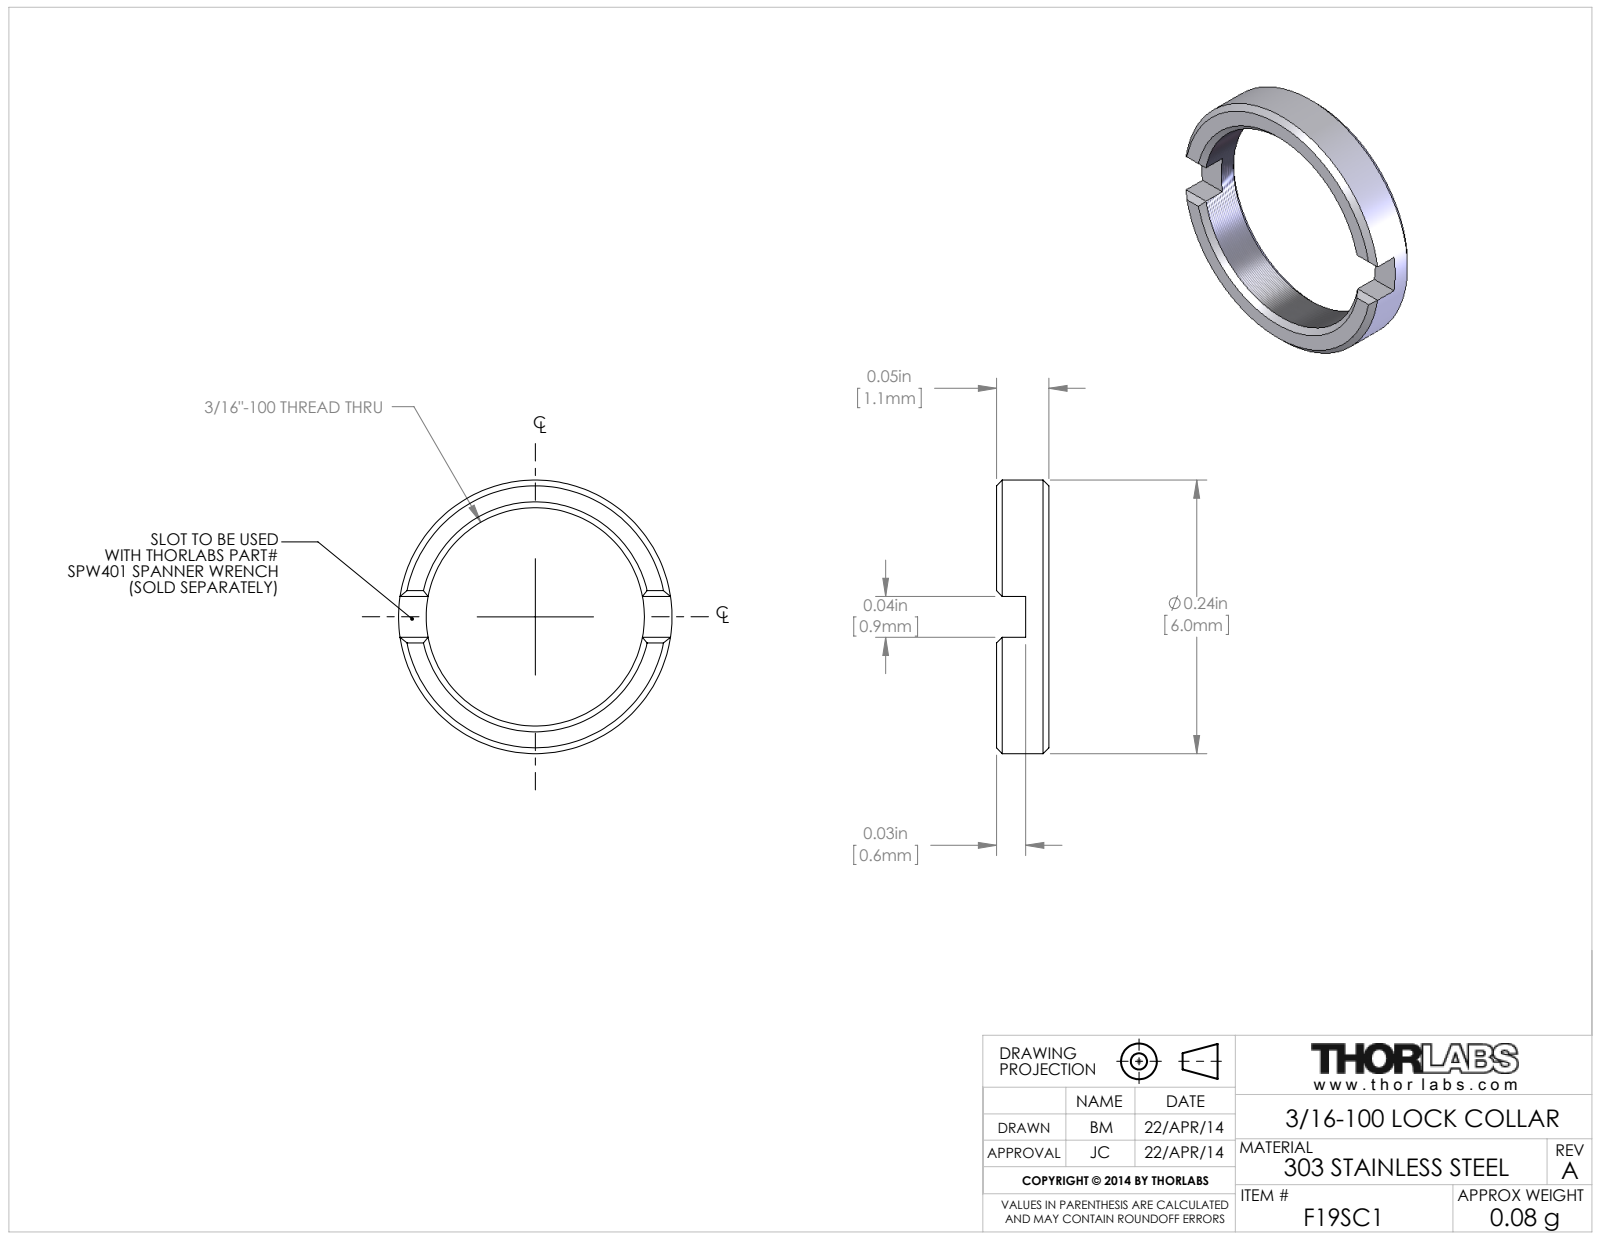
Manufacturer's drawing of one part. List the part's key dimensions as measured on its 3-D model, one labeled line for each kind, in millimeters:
Part name (STEP PRODUCT): TTN024807-E0W
STEP written by: SolidWorks 2012 (AUTOMOTIVE_DESIGN)
Units: millimetres
Bodies: 1 solid, 27 faces (13 planar, 4 cylindrical, 10 other)
Overall size (bounding box): 5.97 × 5.97 × 1.14
Volume: 10 mm³ · Surface area: 53 mm²
Round holes (diameter × count): ⌀4.76 ×1
Round bosses / shafts (diameter × count): ⌀5.97 ×1
Main face-to-face distances: 1.14, 0.51, 0.63, 0.88
